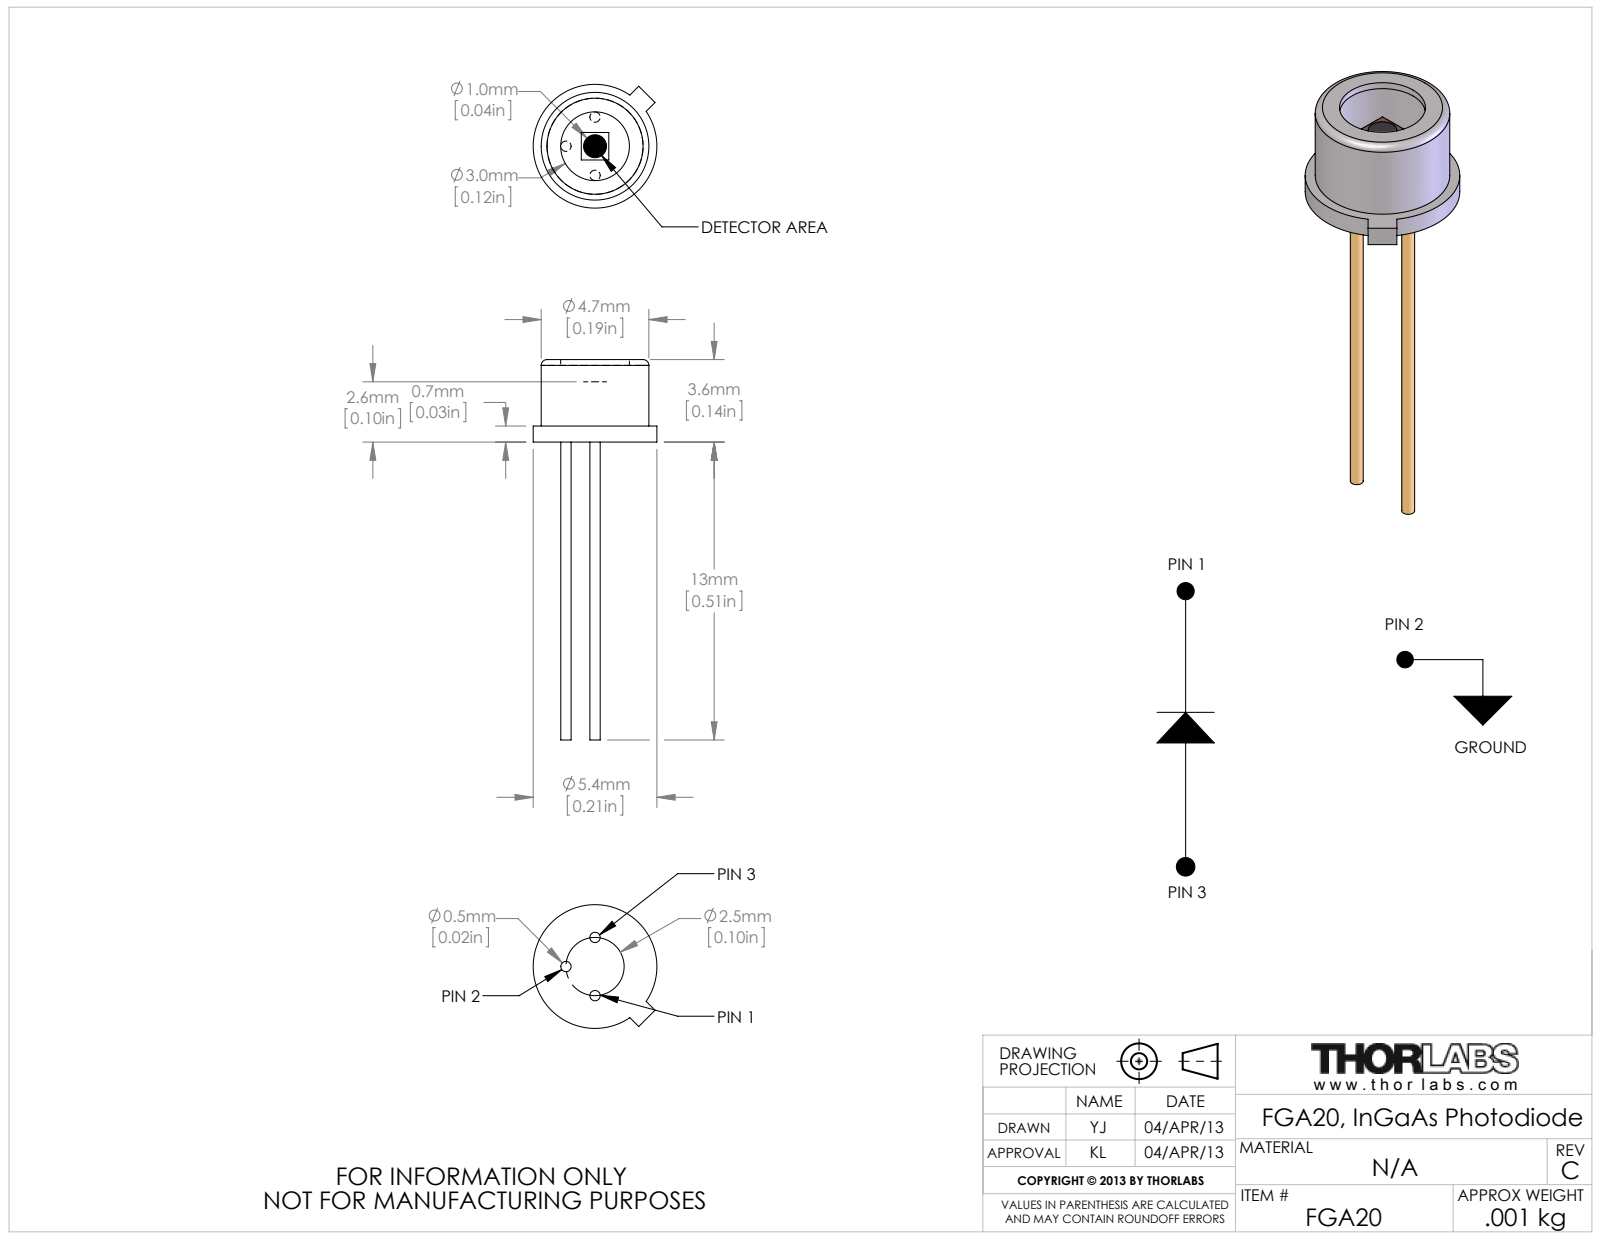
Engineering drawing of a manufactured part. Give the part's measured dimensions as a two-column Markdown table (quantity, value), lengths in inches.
| quantity | value |
| --- | --- |
| part name | 12173-E0W |
| STEP written by | SolidWorks 2012 (AUTOMOTIVE_DESIGN) |
| units | inches |
| bodies | 2 solids, 37 faces (18 planar, 17 cylindrical, 2 other) |
| overall size | 0.654 × 0.213 × 0.213 |
| volume | 0.002 in³ |
| surface area | 0.33 in² |
| round holes (diameter × count) | 0.118 × 1, 0.165 × 1 |
| round bosses / shafts (diameter × count) | 0.018 × 3, 0.213 × 1, 0.185 × 1, 0.039 × 1 |
| main face-to-face distances | 0.018, 0.114, 0.132, 0.142, 0.124, 0.028, 0.104, 0.1, 0.083, 0.073 |
